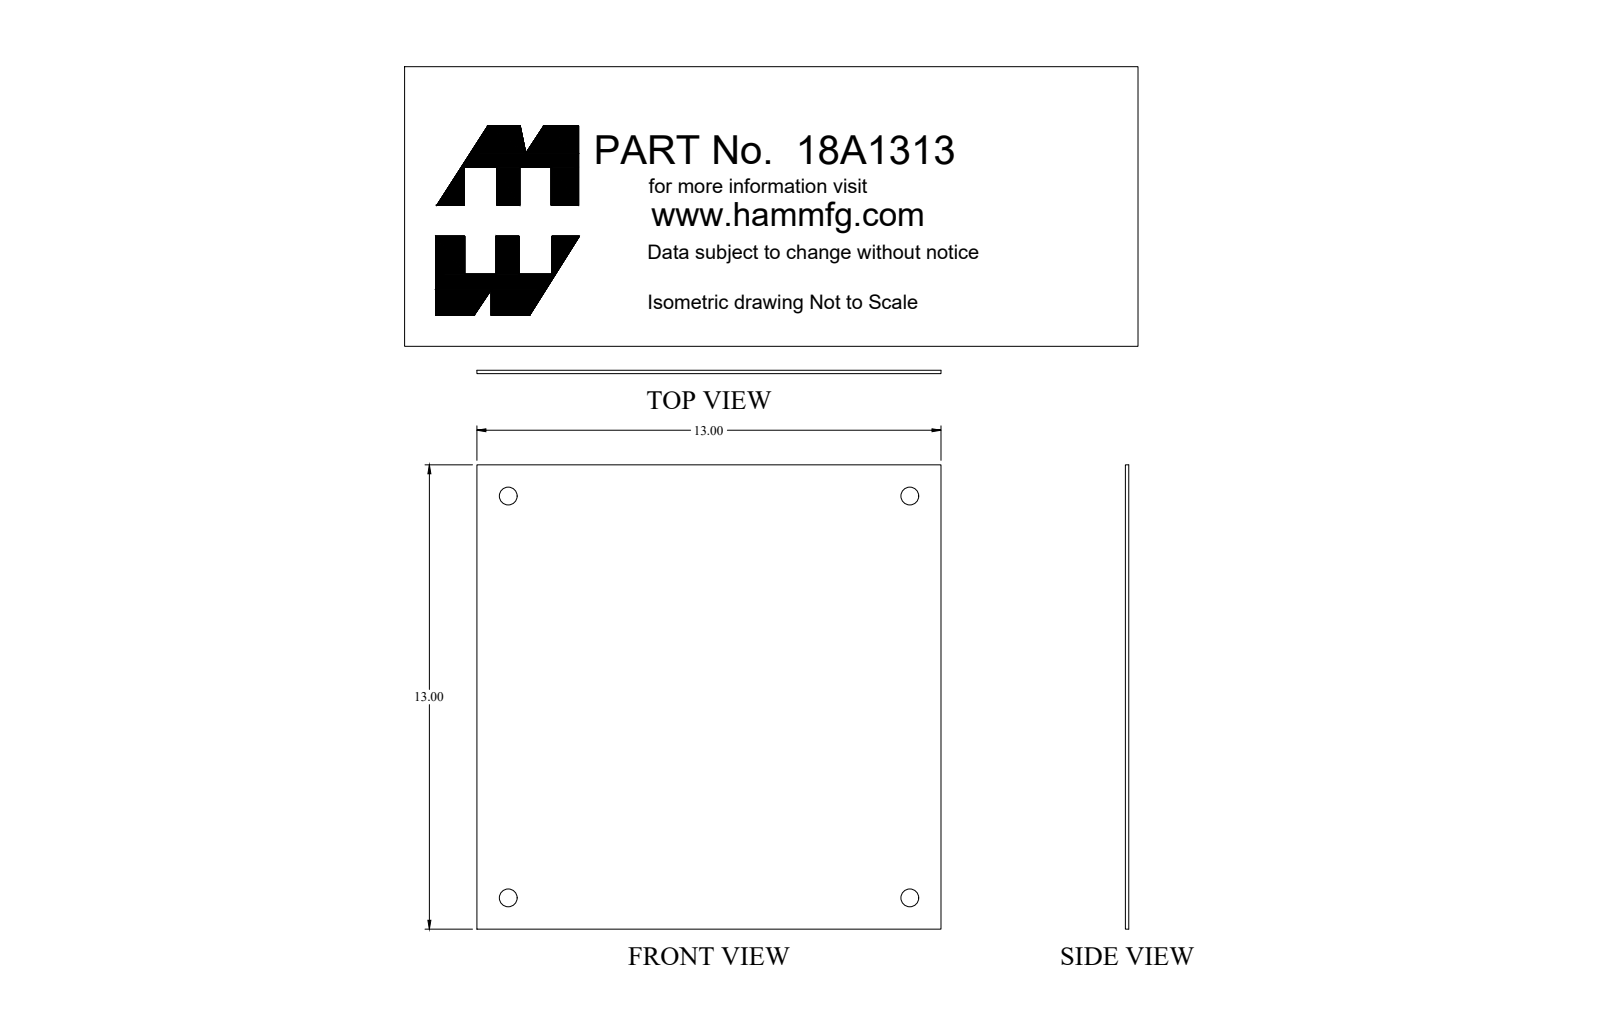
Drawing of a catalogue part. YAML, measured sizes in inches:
part_name: "18A1313"
step_written_by: "SolidWorks 2018 (AUTOMOTIVE_DESIGN)"
units: inches
bodies: {solids: 1, faces: 10, planar: 6, cylindrical: 4, other: 0}
overall_size: [13, 13, 0.095]
volume: 15.98
surface_area: 342
round_holes:
  - {diameter: 0.5, count: 4}
face_to_face_distances: [0.095, 13]
hole_center_spacings: [11.25, 15.911]
